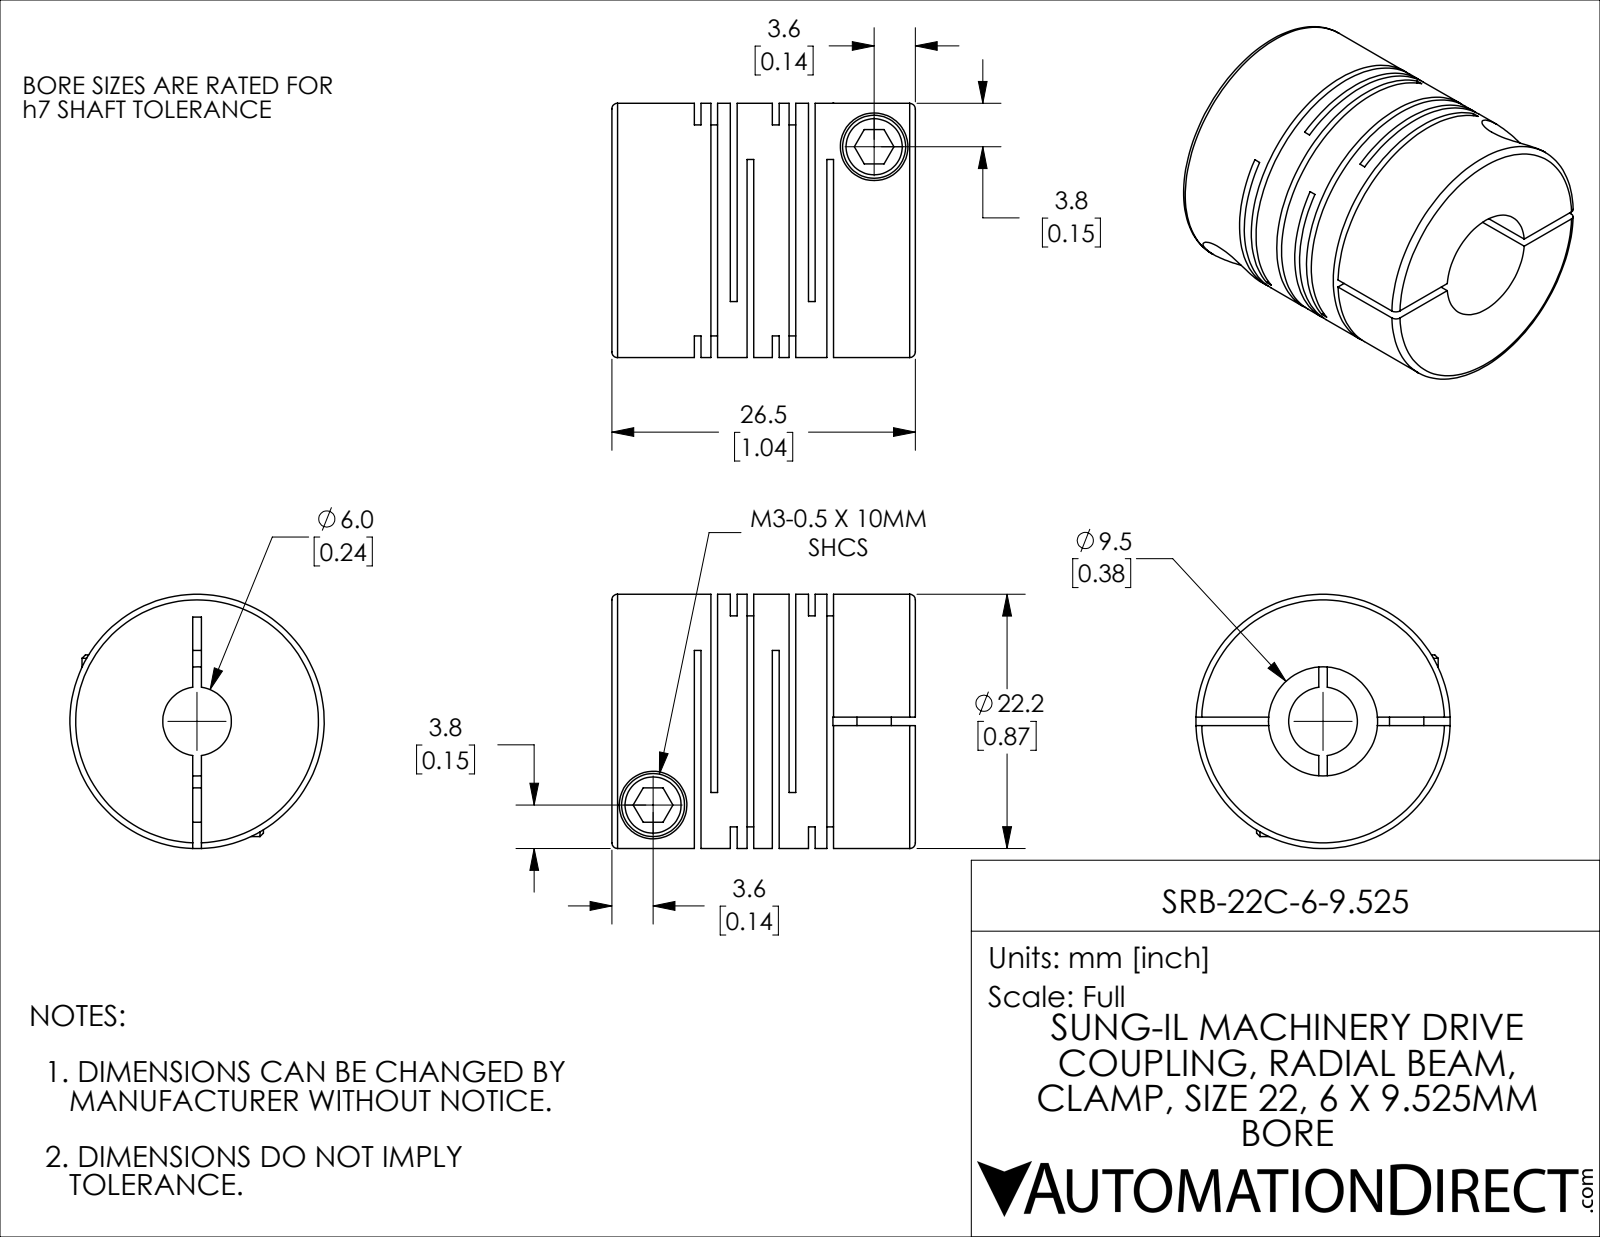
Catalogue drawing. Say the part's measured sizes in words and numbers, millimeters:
The part is named "SRB-22C-6-9.525". Its 3-D file was written by "SolidWorks 2021 (CONFIG_CONTROL_DESIGN)". It is 1 solid with 115 faces: 60 planar, 42 cylindrical and 13 other. Overall it measures 26.5 by 22.2 by 22.2 millimeters. Its volume is 7 160 cubic millimeters and its surface area 7 598 square millimeters. Round holes: 2 of diameter 3, 2 of diameter 5.9, 1 of diameter 6, 1 of diameter 9.53. Round bosses or shafts: 2 of diameter 5.5, 1 of diameter 22.2. The main face-to-face distances are 0.59, 6.82, 1.45, 3.15, 5.37, 3.67, 1.7, 7.41, 6.23, 2.04.
